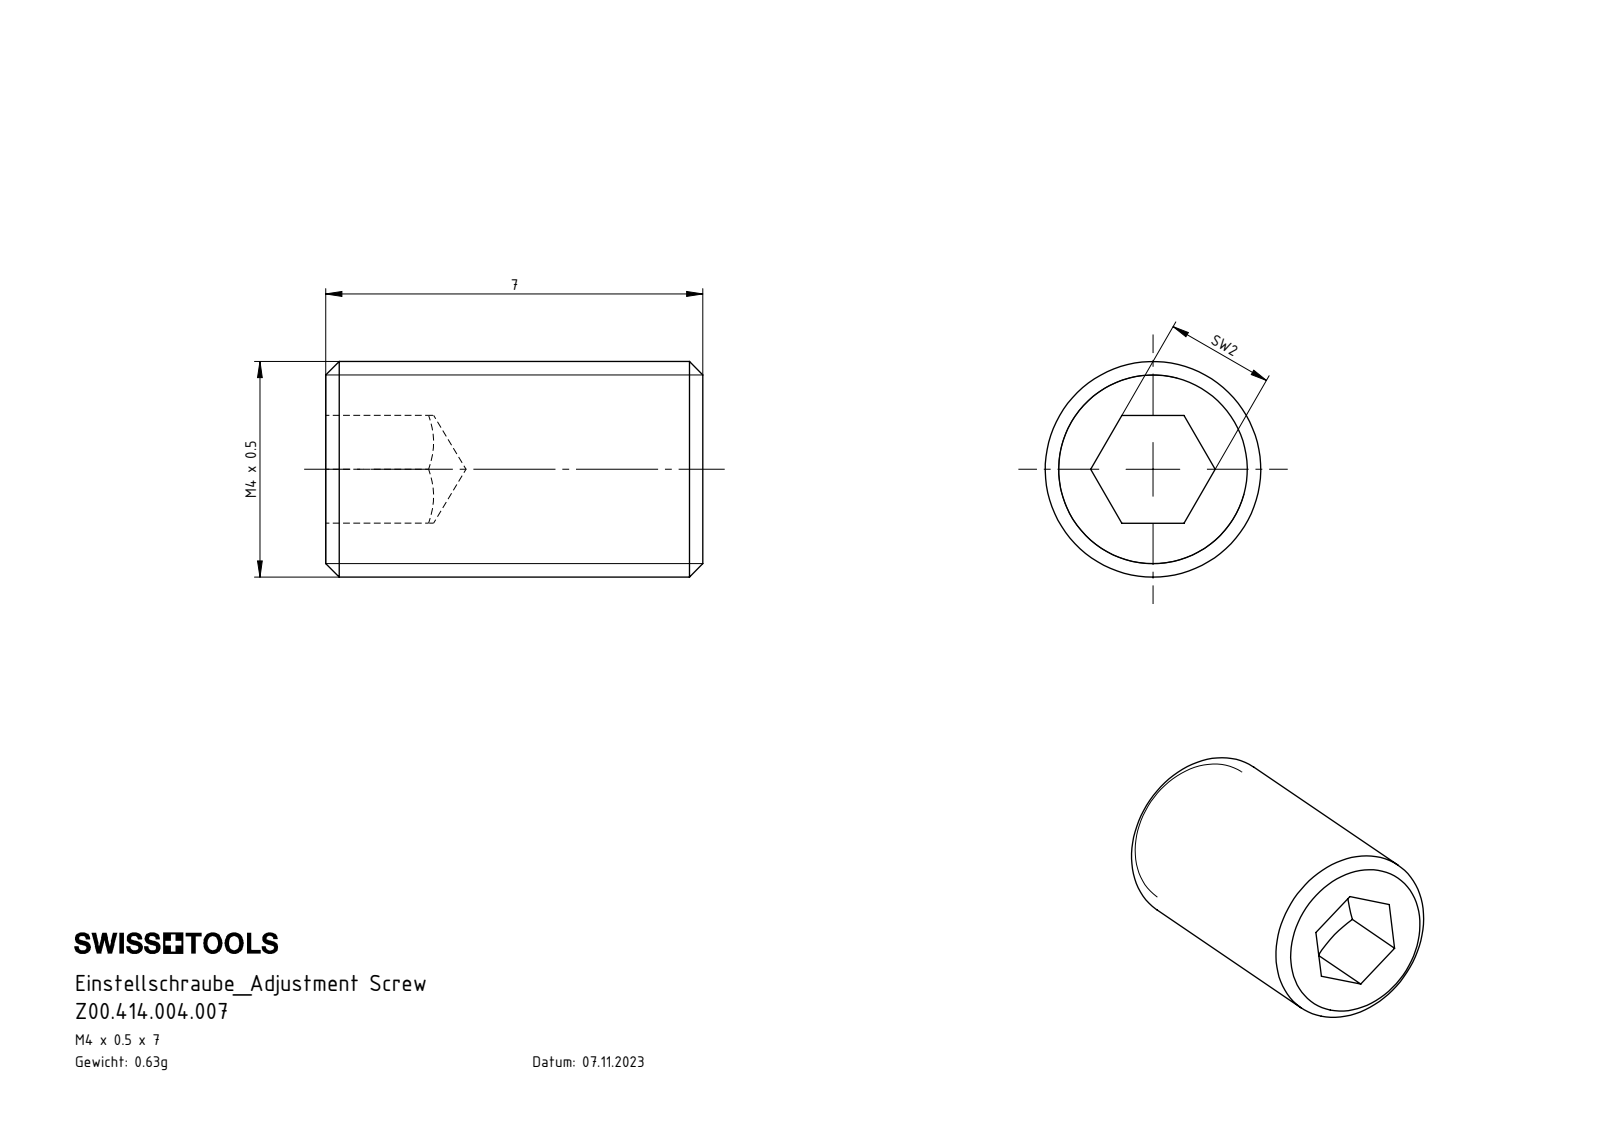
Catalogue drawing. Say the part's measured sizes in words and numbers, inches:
The part is named "Z00.414.004.007". Its 3-D file was written by "SolidWorks 2022 (AUTOMOTIVE_DESIGN)". It is 1 solid with 16 faces: 8 planar, 2 cylindrical and 6 other. Overall it measures 0.276 by 0.157 by 0.157 inches. Its volume is 0.005 cubic inches and its surface area 0.191 square inches. Round bosses or shafts: 1 of diameter 0.157. The main face-to-face distances are 0.079, 0.276.
